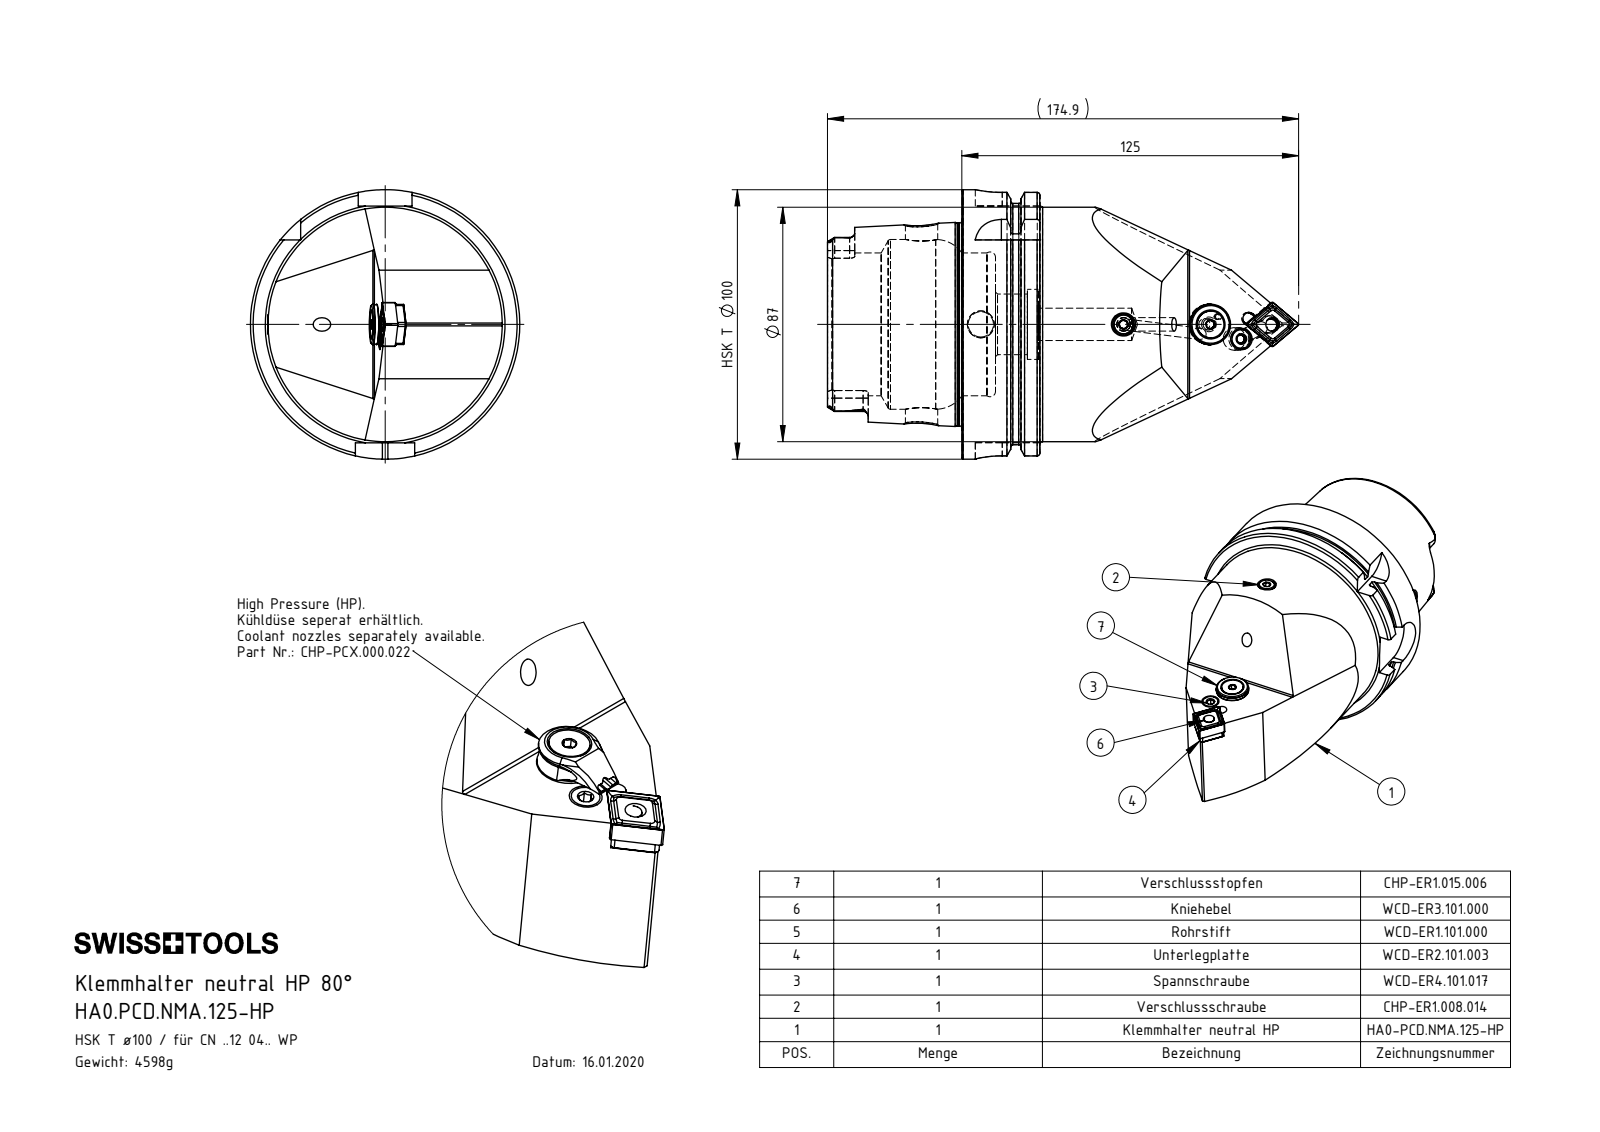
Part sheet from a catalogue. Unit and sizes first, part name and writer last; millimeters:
Units: millimetres
Overall size (bounding box): 174.9 × 100 × 100
Round holes (diameter × count): ⌀4.2 ×2, ⌀5 ×2, ⌀7 ×2, ⌀12 ×2, ⌀1.2 ×1, ⌀2 ×1, ⌀2.5 ×1, ⌀3 ×1, ⌀5.16 ×1, ⌀5.2 ×1, ⌀6.4 ×1, ⌀8.4 ×1
Round bosses / shafts (diameter × count): ⌀8 ×2, ⌀100 ×1, ⌀91.95 ×1, ⌀87 ×1, ⌀75.26 ×1, ⌀15 ×1, ⌀13.4 ×1, ⌀10 ×1
Partial cylindrical surfaces — rounded edges, fillets, slot ends (radius × count): R1.9 ×6, R0.4 ×4, R1 ×4, R4.88 ×4, R10 ×4, R2.5 ×2, R0.8 ×1, R2.1 ×1
Main face-to-face distances: 12.45, 28.95, 16.5, 49.9, 62.35, 78.85, 87.8, 78.2, 28.3, 15.85
Hole centre spacings: 4.51, 4.49, 4.53, 11.6, 11.62, 12.79, 12.85, 12.88
Volume: 584 939 mm³ · Surface area: 73 907 mm²
Bodies: 12 solids, 362 faces (157 planar, 85 cylindrical, 120 other)
Part name (STEP PRODUCT): WCD-ER4.101.017_A; HA0.PCD.NMA.125-HP; CHP-ER1.015.006; CNMG120404 (+8 more)
STEP written by: SolidWorks 2017 (AUTOMOTIVE_DESIGN)
